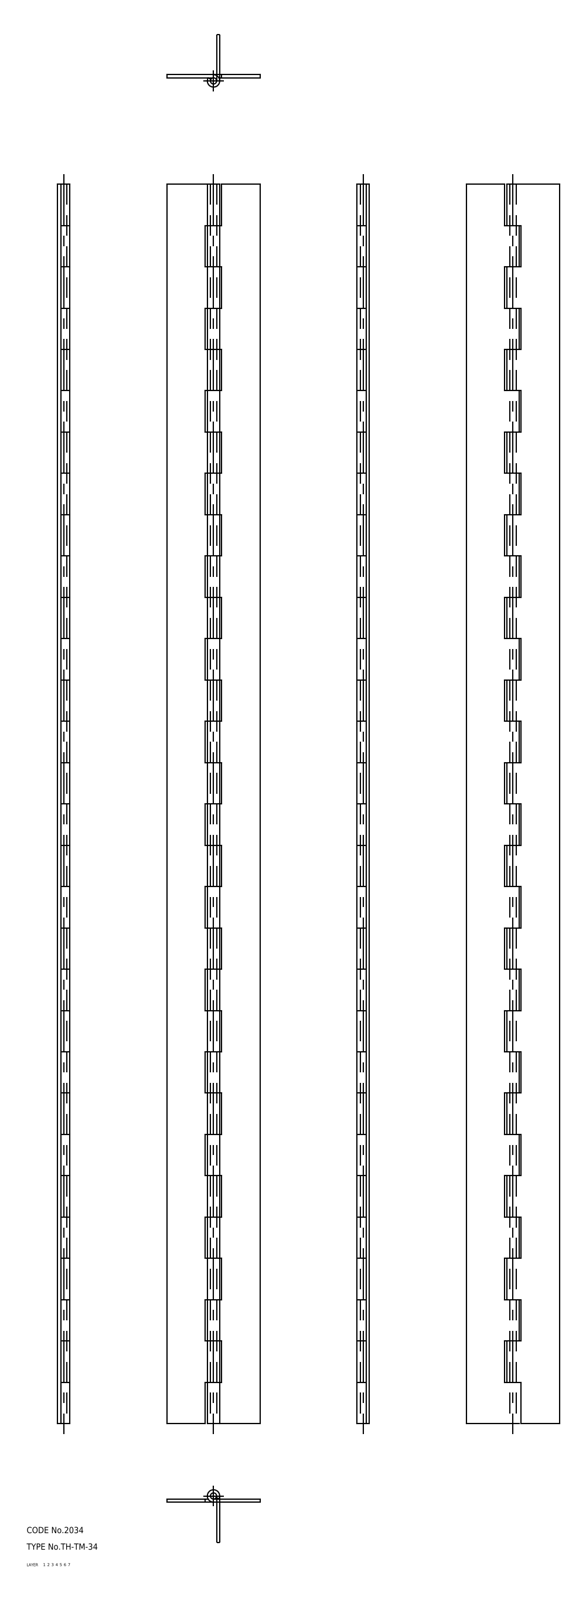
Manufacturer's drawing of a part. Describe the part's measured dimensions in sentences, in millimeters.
The part is named "shaft; hinge piece_B; hinge piece_A; TH_TM_34_22820_36". Its 3-D file was written by "CADfix (AUTOMOTIVE_DESIGN)". It is 3 solids with 192 faces: 0 planar, 0 cylindrical and 192 other. Overall it measures 600 by 45 by 6 millimeters. Its volume is 51 714 cubic millimeters and its surface area 74 088 square millimeters.
